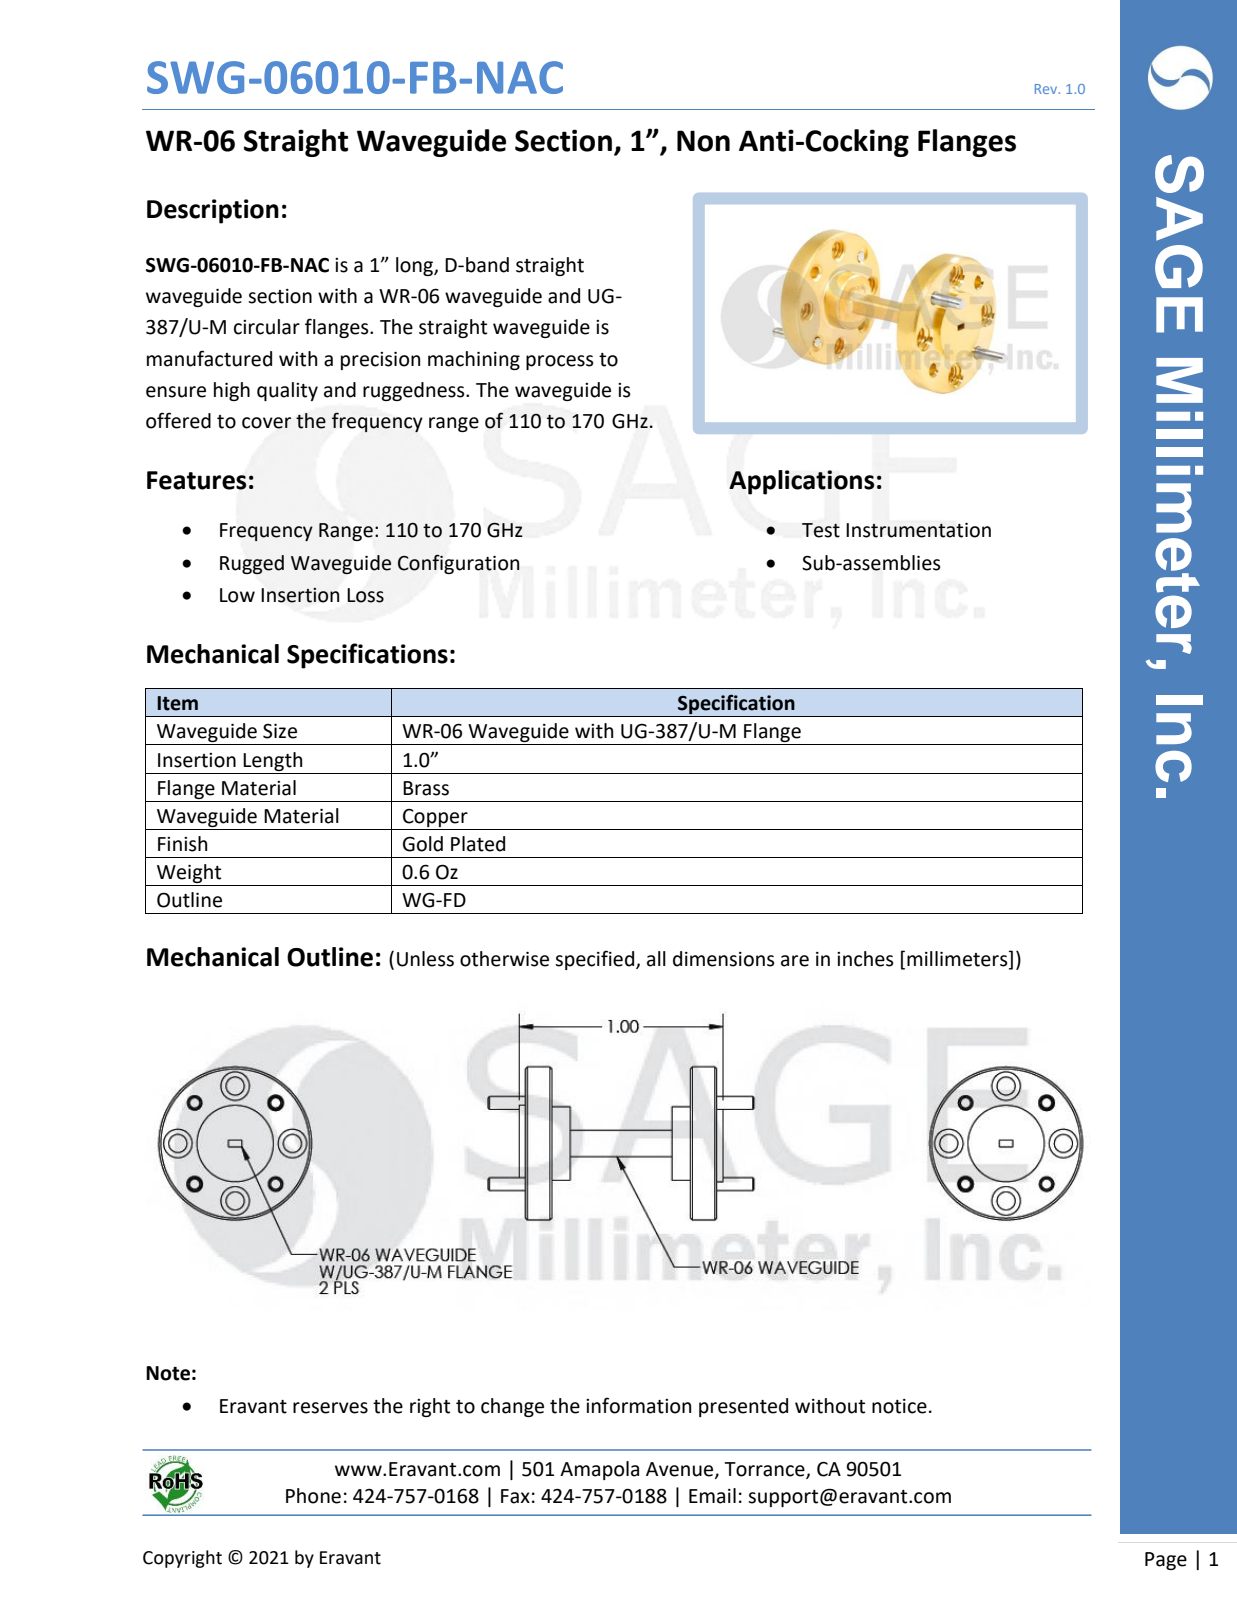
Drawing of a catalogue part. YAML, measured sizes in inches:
part_name: "SWG-06010-F1"
step_written_by: "SolidWorks 2013 (CONFIG_CONTROL_DESIGN)"
units: inches
bodies: {solids: 5, faces: 140, planar: 32, cylindrical: 68, other: 40}
overall_size: [1.305, 0.75, 0.75]
volume: 0.141
surface_area: 3.686
round_holes:
  - {diameter: 0.061, count: 4}
  - {diameter: 0.067, count: 4}
  - {diameter: 0.089, count: 4}
  - {diameter: 0.14, count: 4}
round_bosses_or_shafts:
  - {diameter: 0.063, count: 4}
  - {diameter: 0.75, count: 1}
  - {diameter: 0.375, count: 1}
  - {diameter: 0.36, count: 1}
face_to_face_distances: [0.13, 0.81, 0.68, 0.94, 0.03, 0.16, 0.84, 0.97, 0.25, 0.75]
hole_center_spacings: [0.215, 0.398, 0.519, 0.562]
